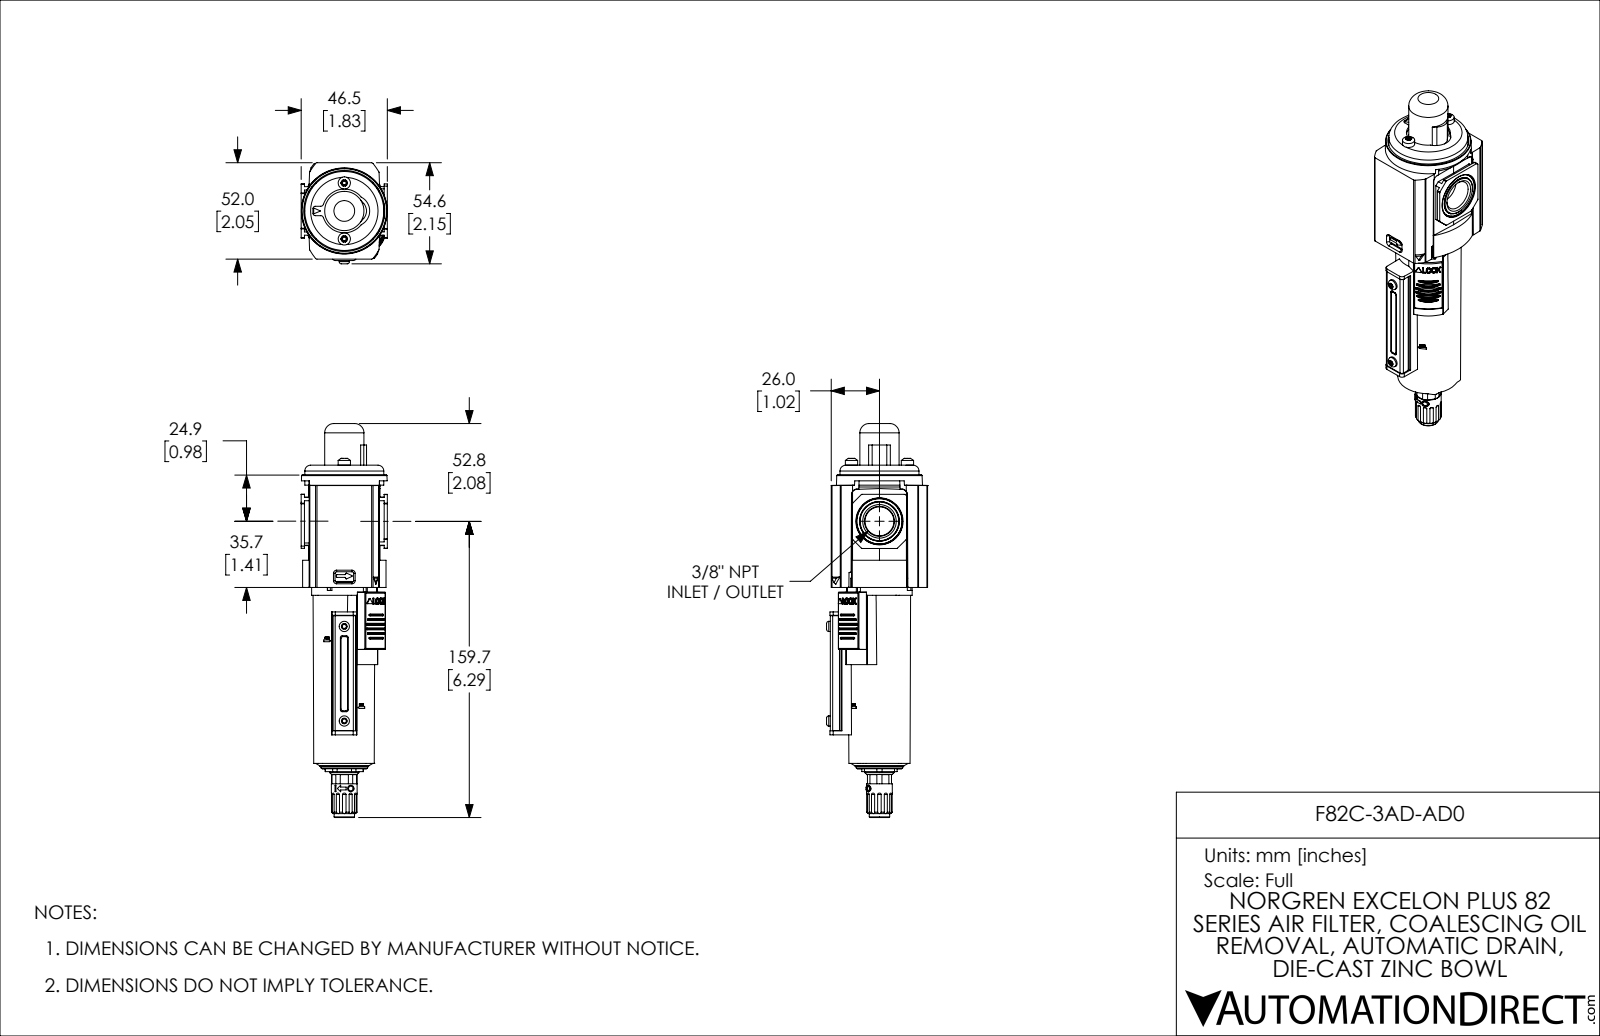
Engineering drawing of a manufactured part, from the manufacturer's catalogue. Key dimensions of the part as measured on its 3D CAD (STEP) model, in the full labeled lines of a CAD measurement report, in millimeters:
Part name (STEP PRODUCT): F82C-3AD-AD0
STEP written by: SolidWorks 2021 (CONFIG_CONTROL_DESIGN)
Units: millimetres
Bodies: 8 solids, 1241 faces (520 planar, 506 cylindrical, 215 other)
Overall size (bounding box): 212.5 × 54.6 × 46.5
Volume: 227 100 mm³ · Surface area: 60 970 mm²
Round holes (diameter × count): ⌀1.5 ×2, ⌀2 ×2, ⌀3.3 ×2, ⌀4.4 ×2, ⌀2.5 ×1, ⌀6.6 ×1, ⌀16 ×1
Round bosses / shafts (diameter × count): ⌀6.6 ×2, ⌀5.5 ×2, ⌀4 ×2, ⌀42.6 ×1, ⌀38.7 ×1, ⌀35.3 ×1, ⌀34.4 ×1, ⌀32.8 ×1
Partial cylindrical surfaces — rounded edges, fillets, slot ends (radius × count): R0.5 ×73, R1 ×50, R0.3 ×12, R0.5 ×12, R0.3 ×10, R0.8 ×8, R0.9 ×8, R1.2 ×8
Main face-to-face distances: 1.5, 50.5, 52, 49, 48.2, 4.6, 34.3, 37.5, 3.1, 32.8
Hole centre spacings: 20.2, 13.5, 15.1, 15.1, 30.2, 27, 30.2, 30.2
